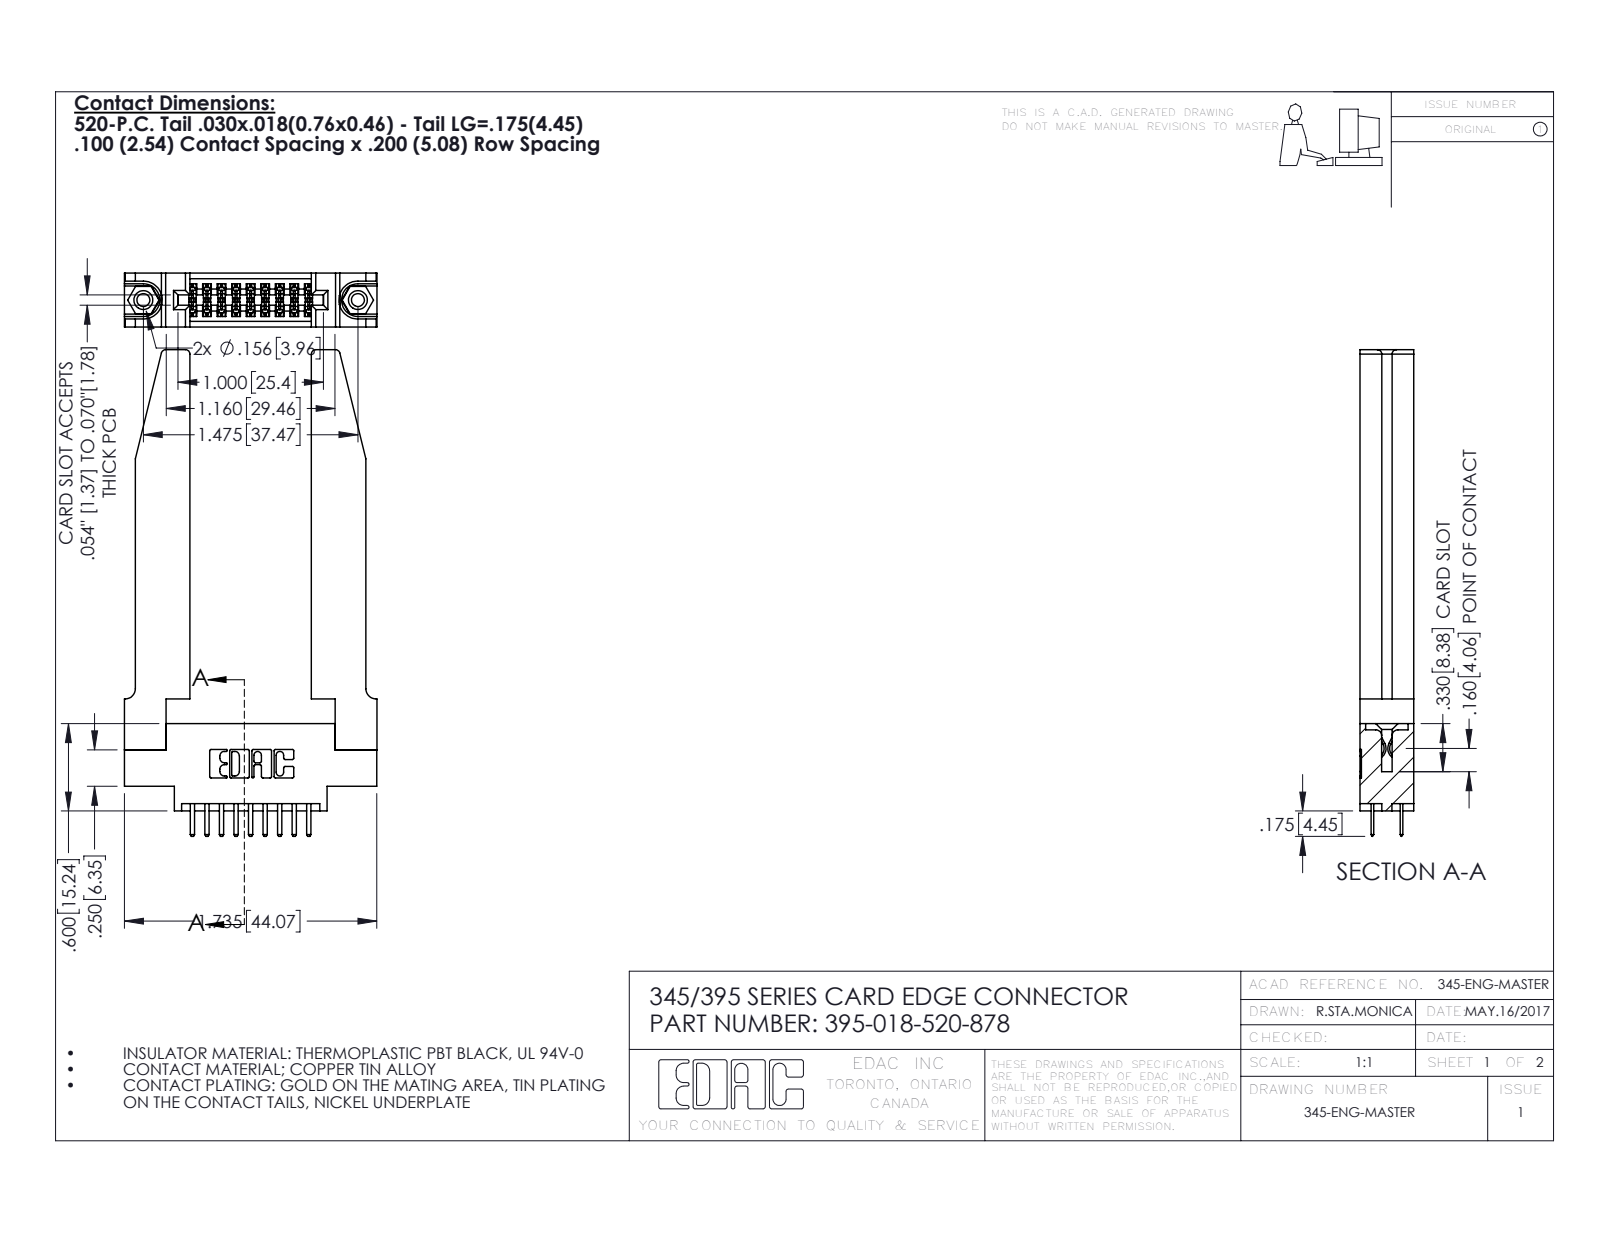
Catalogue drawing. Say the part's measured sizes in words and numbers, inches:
The part is named "345-220-078_345-220-078; 345-292-001_345-293-120; 345-250-001_345-250-001-102; 395-018-520-878 (+1 more)". Its 3-D file was written by "SolidWorks 2016 (CONFIG_CONTROL_DESIGN)". It is 23 solids with 1336 faces: 856 planar, 428 cylindrical and 52 other. Overall it measures 3.345 by 1.736 by 0.37 inches. Its volume is 0.709 cubic inches and its surface area 18.64 square inches. Round holes: 2 of diameter 0.089, 2 of diameter 0.125, 2 of diameter 0.156, 1 of diameter 0.064. Round bosses or shafts: 2 of diameter 0.155. Partial cylindrical surfaces (rounded edges, fillets, slot ends): 27 of radius 0.006, 22 of radius 0.01, 22 of radius 0.01, 8 of radius 0.03, 6 of radius 0.007, 6 of radius 0.031, 3 of radius 0.026, 2 of radius 0.014. The main face-to-face distances are 0.37, 0.072, 0.298, 0.15, 0.22, 0.077, 0.148, 0.835, 0.2, 0.095. The hole center spacings are 0.27, 1.244, 1.475.
